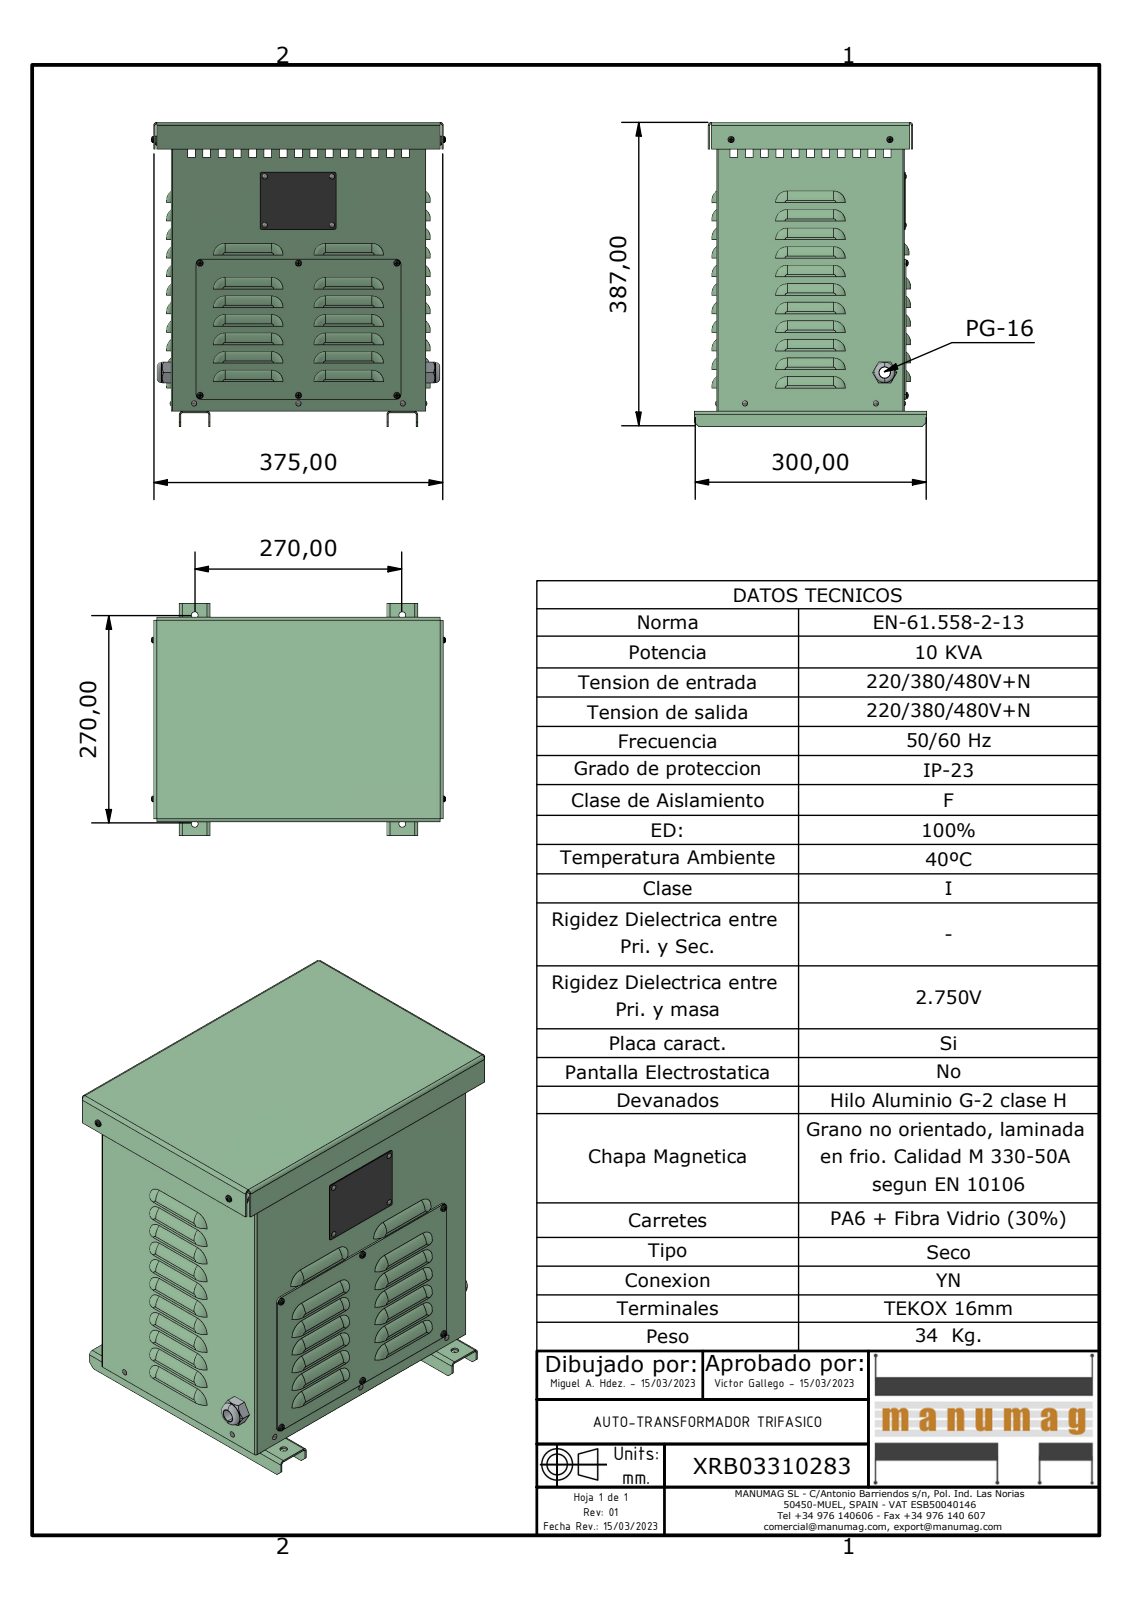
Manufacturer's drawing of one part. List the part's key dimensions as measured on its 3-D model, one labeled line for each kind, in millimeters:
Part name (STEP PRODUCT): XRB03310283; JE010 EXPORT BASE; JE010 EXPORT PATA; JE010 EXPORT CUERPO (+6 more)
STEP written by: Autodesk Inventor 2023 (AUTOMOTIVE_DESIGN)
Units: millimetres
Bodies: 33 solids, 1975 faces (1082 planar, 421 cylindrical, 472 other)
Overall size (bounding box): 394.02 × 381.14 × 300
Volume: 1 720 000 mm³ · Surface area: 1 517 000 mm²
Round holes (diameter × count): ⌀2.3 ×8, ⌀3.7 ×8, ⌀8.8 ×8, ⌀4.3 ×5, ⌀3.4 ×4, ⌀4 ×4, ⌀5 ×3, ⌀14 ×1, ⌀24 ×1
Round bosses / shafts (diameter × count): ⌀3.2 ×9, ⌀4 ×8, ⌀3.62 ×8, ⌀26 ×1, ⌀23 ×1, ⌀22.5 ×1
Partial cylindrical surfaces — rounded edges, fillets, slot ends (radius × count): R14 ×105, R4 ×68, R15 ×40, R2 ×20, R1.5 ×6, R2 ×5, R6 ×4
Main face-to-face distances: 2, 240.62, 327.32, 372.01, 242.62, 374.01, 238.62, 325.32, 329.32, 4
Hole centre spacings: 55.99, 127.3, 168.89, 210.03, 213.21, 213.3, 342.86, 62.98
